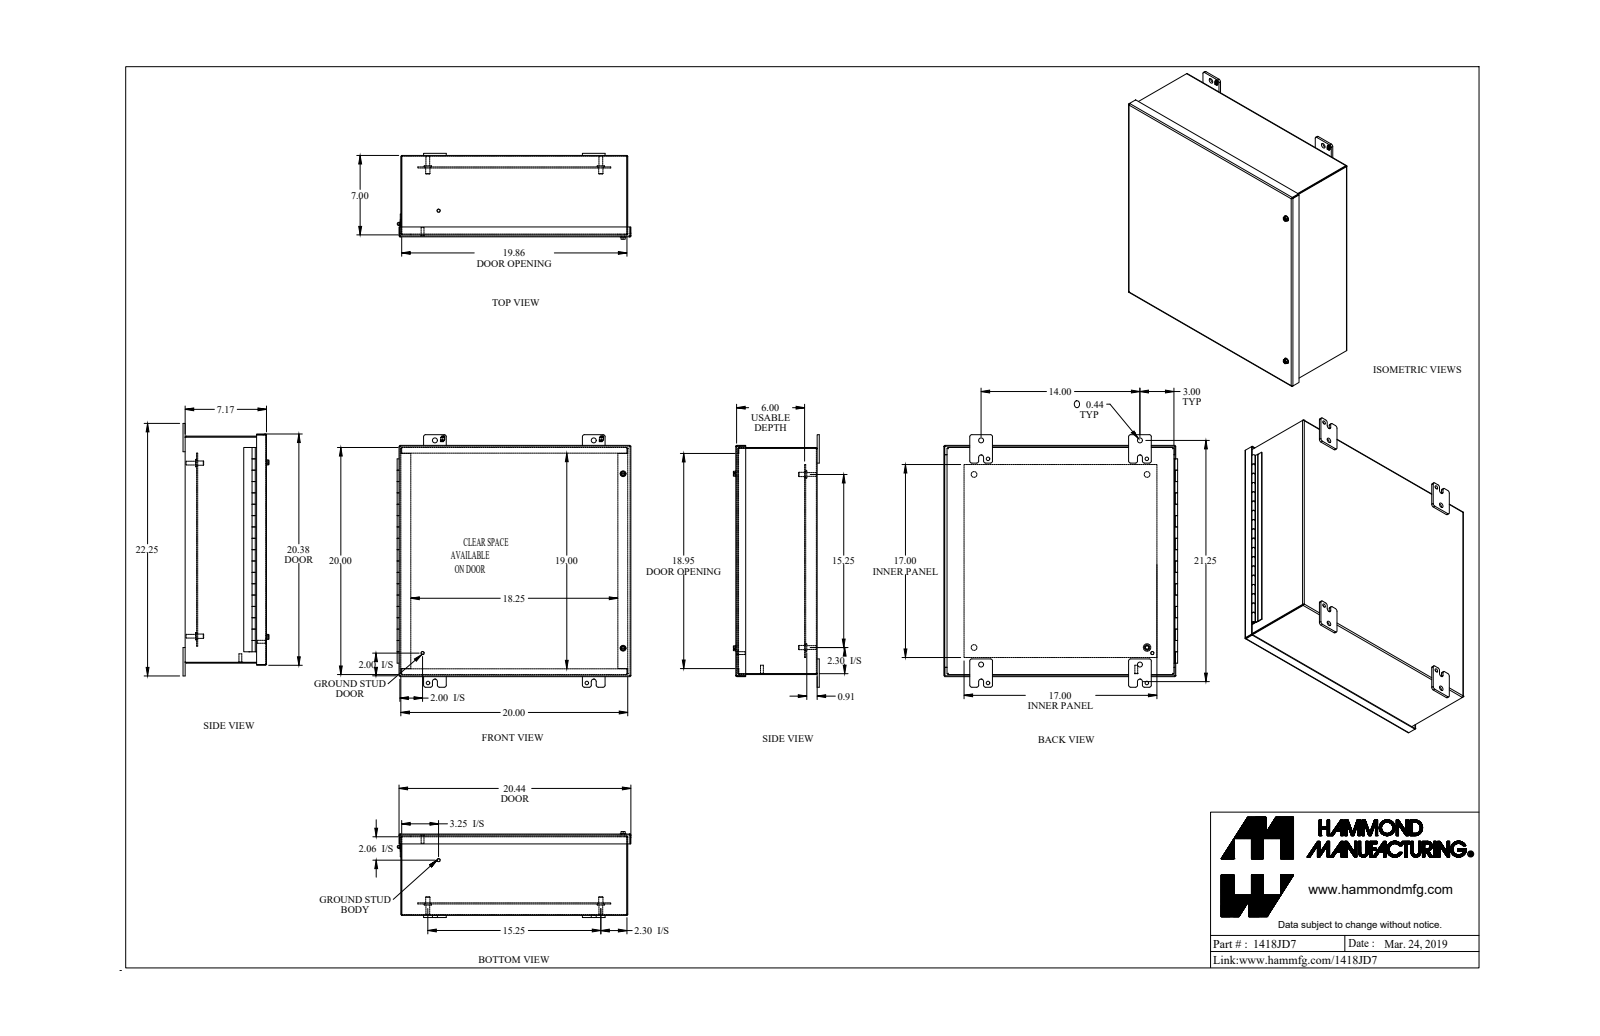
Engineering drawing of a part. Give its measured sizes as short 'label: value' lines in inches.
name: 1418JD7_Default
written by: SolidWorks 2018 (CONFIG_CONTROL_DESIGN)
unit: in
bodies: 32 solids, 880 faces (545 planar, 293 cylindrical, 42 other)
size: 22.25 × 20.604 × 7.571
volume: 163.3 in³; area: 4 001 in²
holes: 6× ⌀0.313, 4× ⌀0.437, 4× ⌀0.5, 2× ⌀0.26, 2× ⌀0.266, 2× ⌀0.28, 2× ⌀0.29, 2× ⌀0.307, 2× ⌀0.397, 2× ⌀0.445, 1× ⌀0.187, 1× ⌀3.5
bosses: 4× ⌀0.65, 4× ⌀0.375, 4× ⌀0.33, 2× ⌀1, 2× ⌀0.51, 2× ⌀0.5, 2× ⌀0.39, 2× ⌀0.281
rounds: 24× R0.188, 20× R0.25, 12× R0.036, 12× R0.108, 8× R0.218, 6× R0.133, 5× R0.06, 4× R0.5
face distances: 0.072, 7.1, 19.928, 7.172, 7.028, 6.091, 1.104, 1.032, 5.996, 6.068
hole spacings: 15.25, 21.567, 1.736, 14, 19.75, 24.209, 1.907, 1.966
